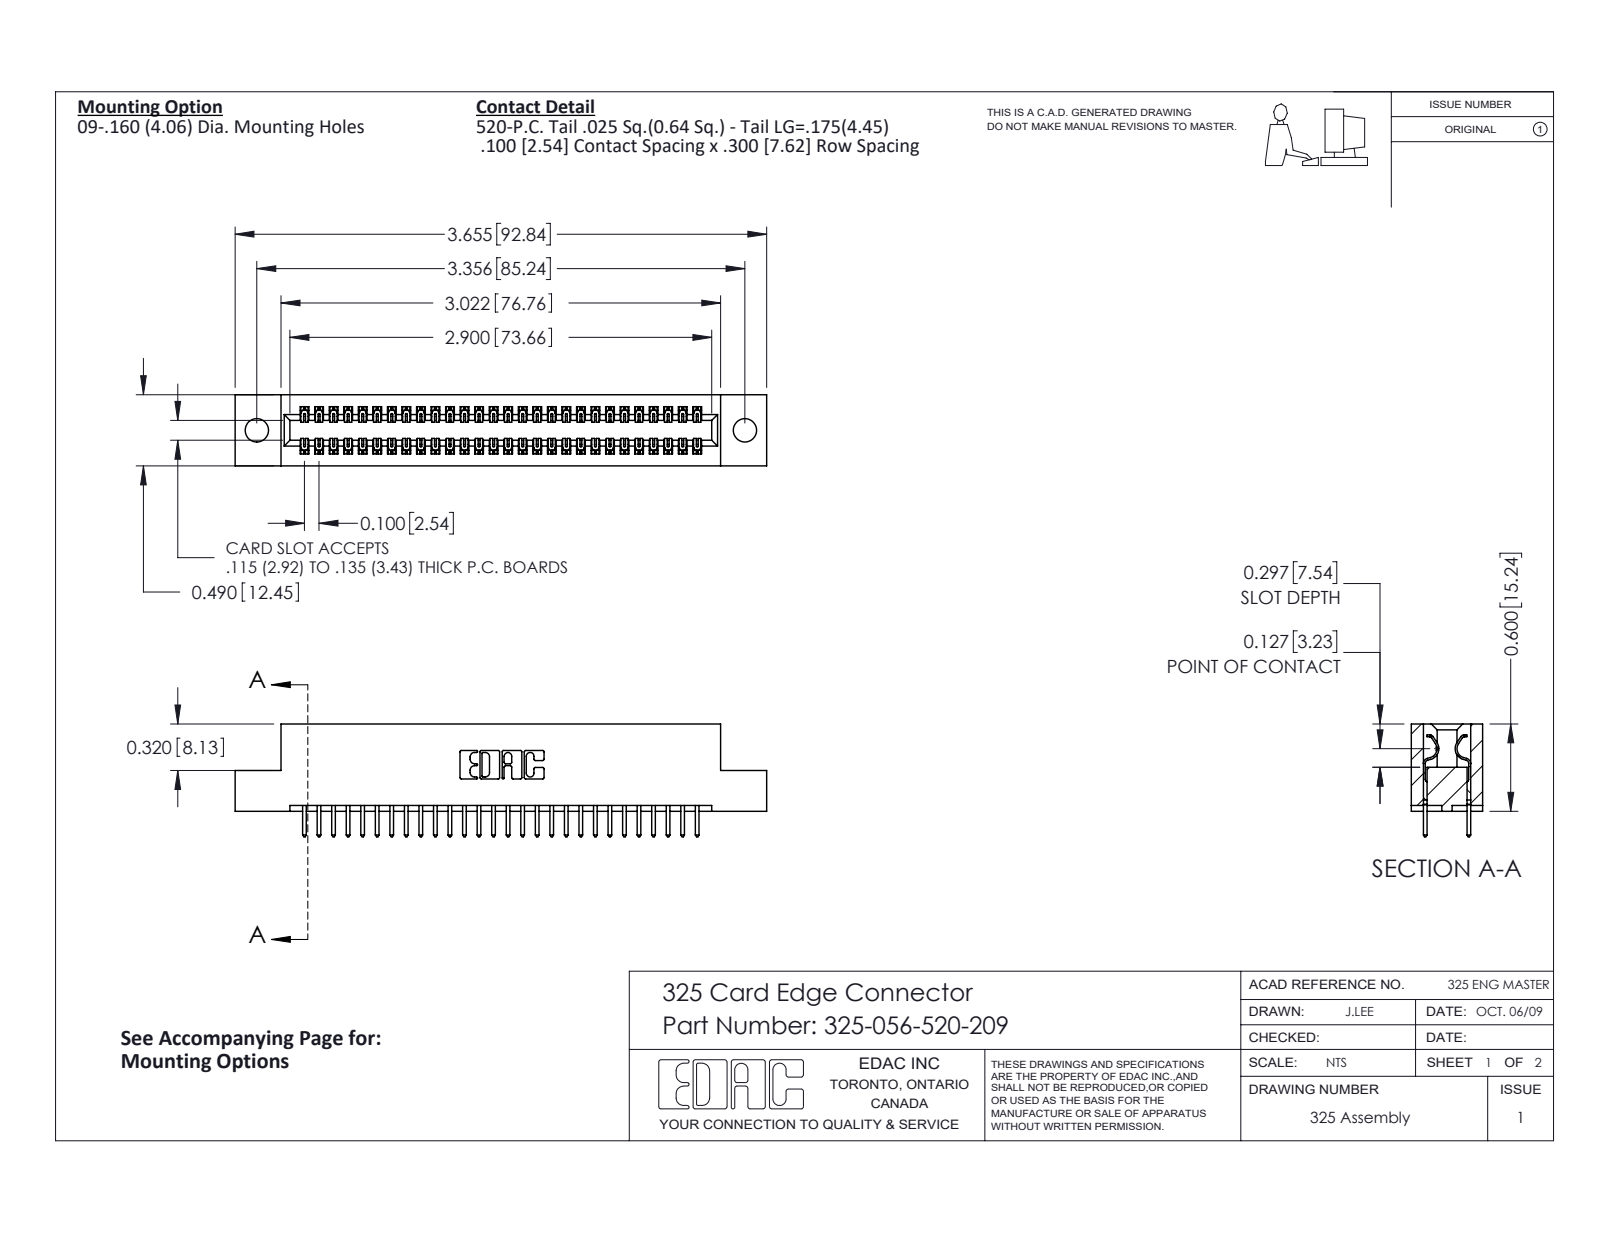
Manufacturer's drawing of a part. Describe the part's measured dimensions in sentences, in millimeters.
The part is named "325 Part_.160 TH; 325-292-001_325-293-120; 325-056-520-209". Its 3-D file was written by "SolidWorks 2016 (CONFIG_CONTROL_DESIGN)". It is 57 solids with 3026 faces: 2086 planar, 940 cylindrical and 0 other. Overall it measures 92.8 by 19.7 by 12.4 millimeters. Its volume is 11 600 cubic millimeters and its surface area 13 540 square millimeters. Round holes: 2 of diameter 4.1. Partial cylindrical surfaces (rounded edges, fillets, slot ends): 84 of radius 0.2, 56 of radius 0.3, 22 of radius 0.3, 6 of radius 0.2, 6 of radius 0.8, 3 of radius 0.7, 2 of radius 0.4, 2 of radius 0.6. The main face-to-face distances are 2.1, 10.3, 12.4, 7.6, 2.7, 9.7, 0.6, 8.3, 7, 1. The hole center spacings are 85.2.
